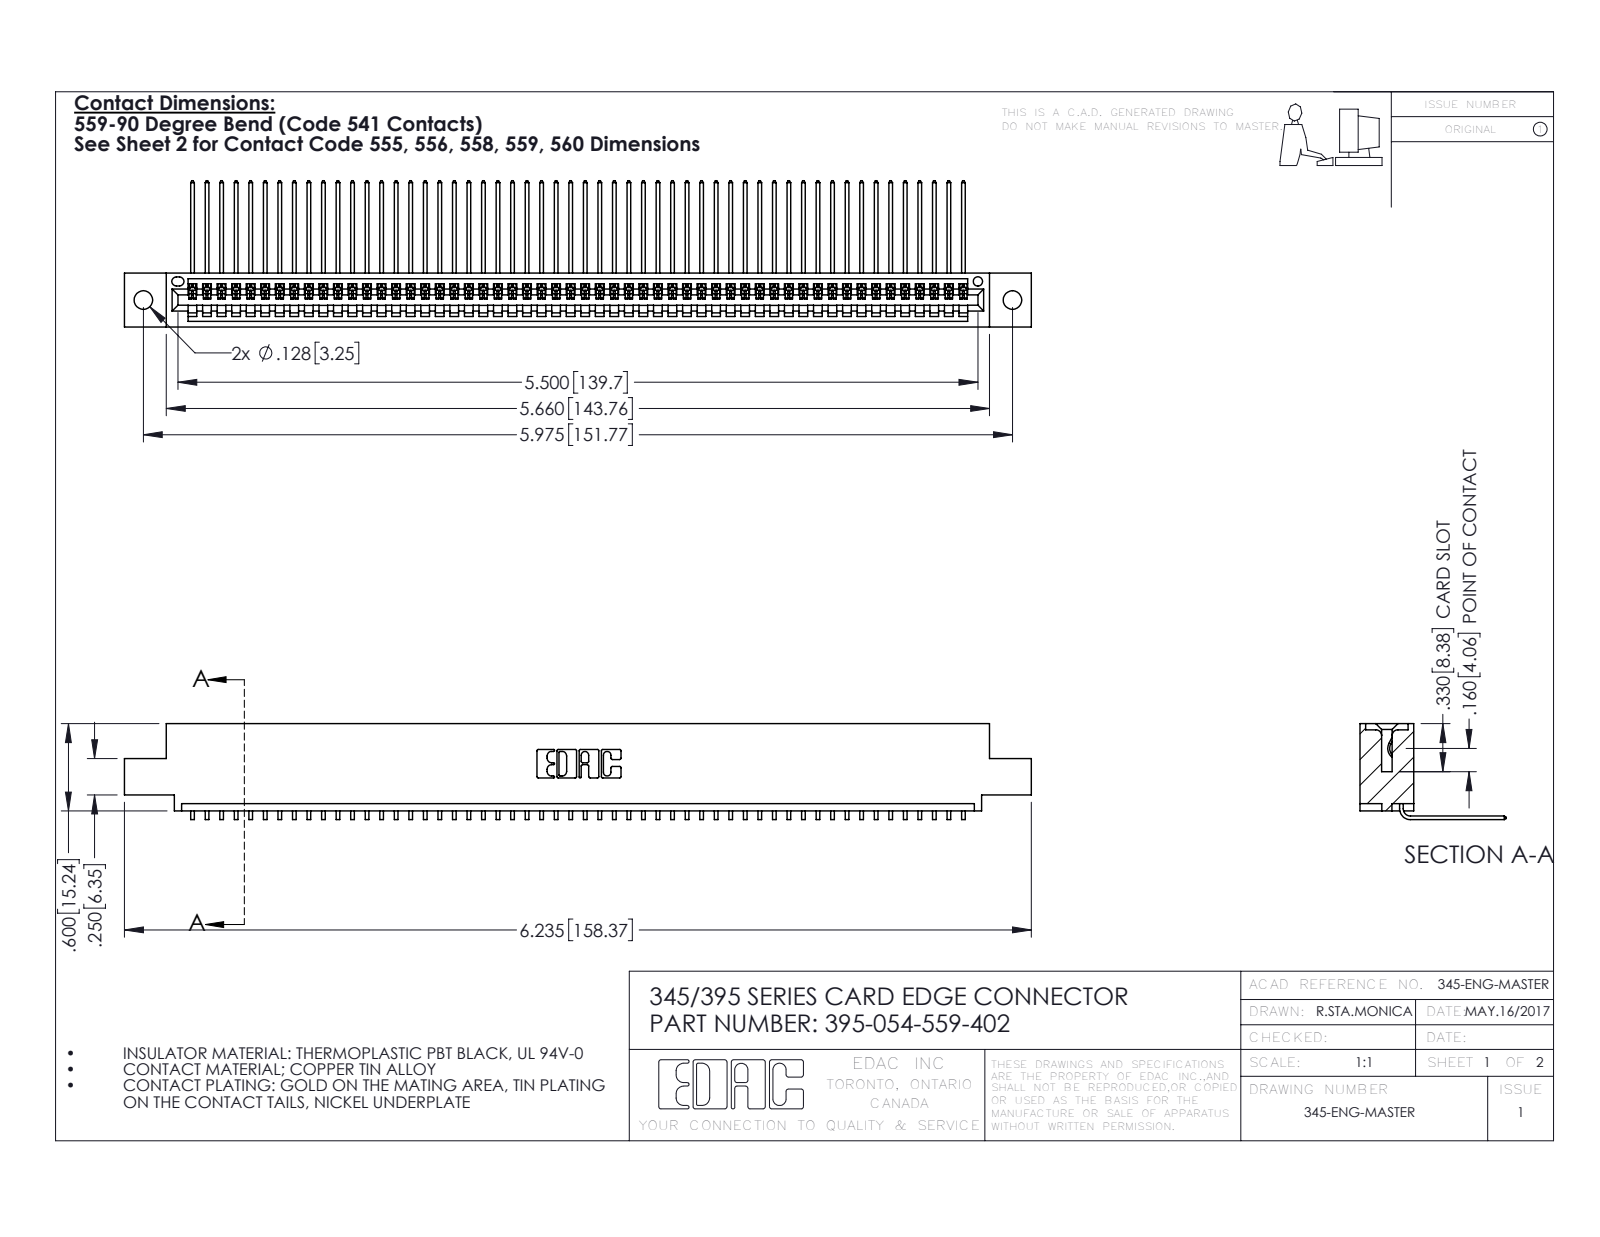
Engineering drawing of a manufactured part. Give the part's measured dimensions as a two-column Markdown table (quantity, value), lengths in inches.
| quantity | value |
| --- | --- |
| part name | 345 Part_0.110 Offset - 0.128 Dia; 345-292-001_558 559 Tail - 1; 395-054-559-402 |
| STEP written by | SolidWorks 2016 (CONFIG_CONTROL_DESIGN) |
| units | inches |
| bodies | 55 solids, 3370 faces (2352 planar, 1018 cylindrical, 0 other) |
| overall size | 6.235 × 1.005 × 0.659 |
| volume | 0.928 in³ |
| surface area | 32.93 in² |
| round holes (diameter × count) | 0.128 × 2, 0.064 × 1 |
| partial cylindrical surfaces (radius × count) | 0.006 × 108, 0.01 × 22, 0.007 × 6, 0.031 × 6, 0.026 × 3, 0.031 × 2, 0.04 × 2, 0.014 × 1 |
| main face-to-face distances | 0.072, 0.298, 0.37, 0.2, 0.098, 0.272, 0.025, 0.225, 0.149, 0.072 |
| hole center spacings | 0.27, 5.739, 5.975 |
